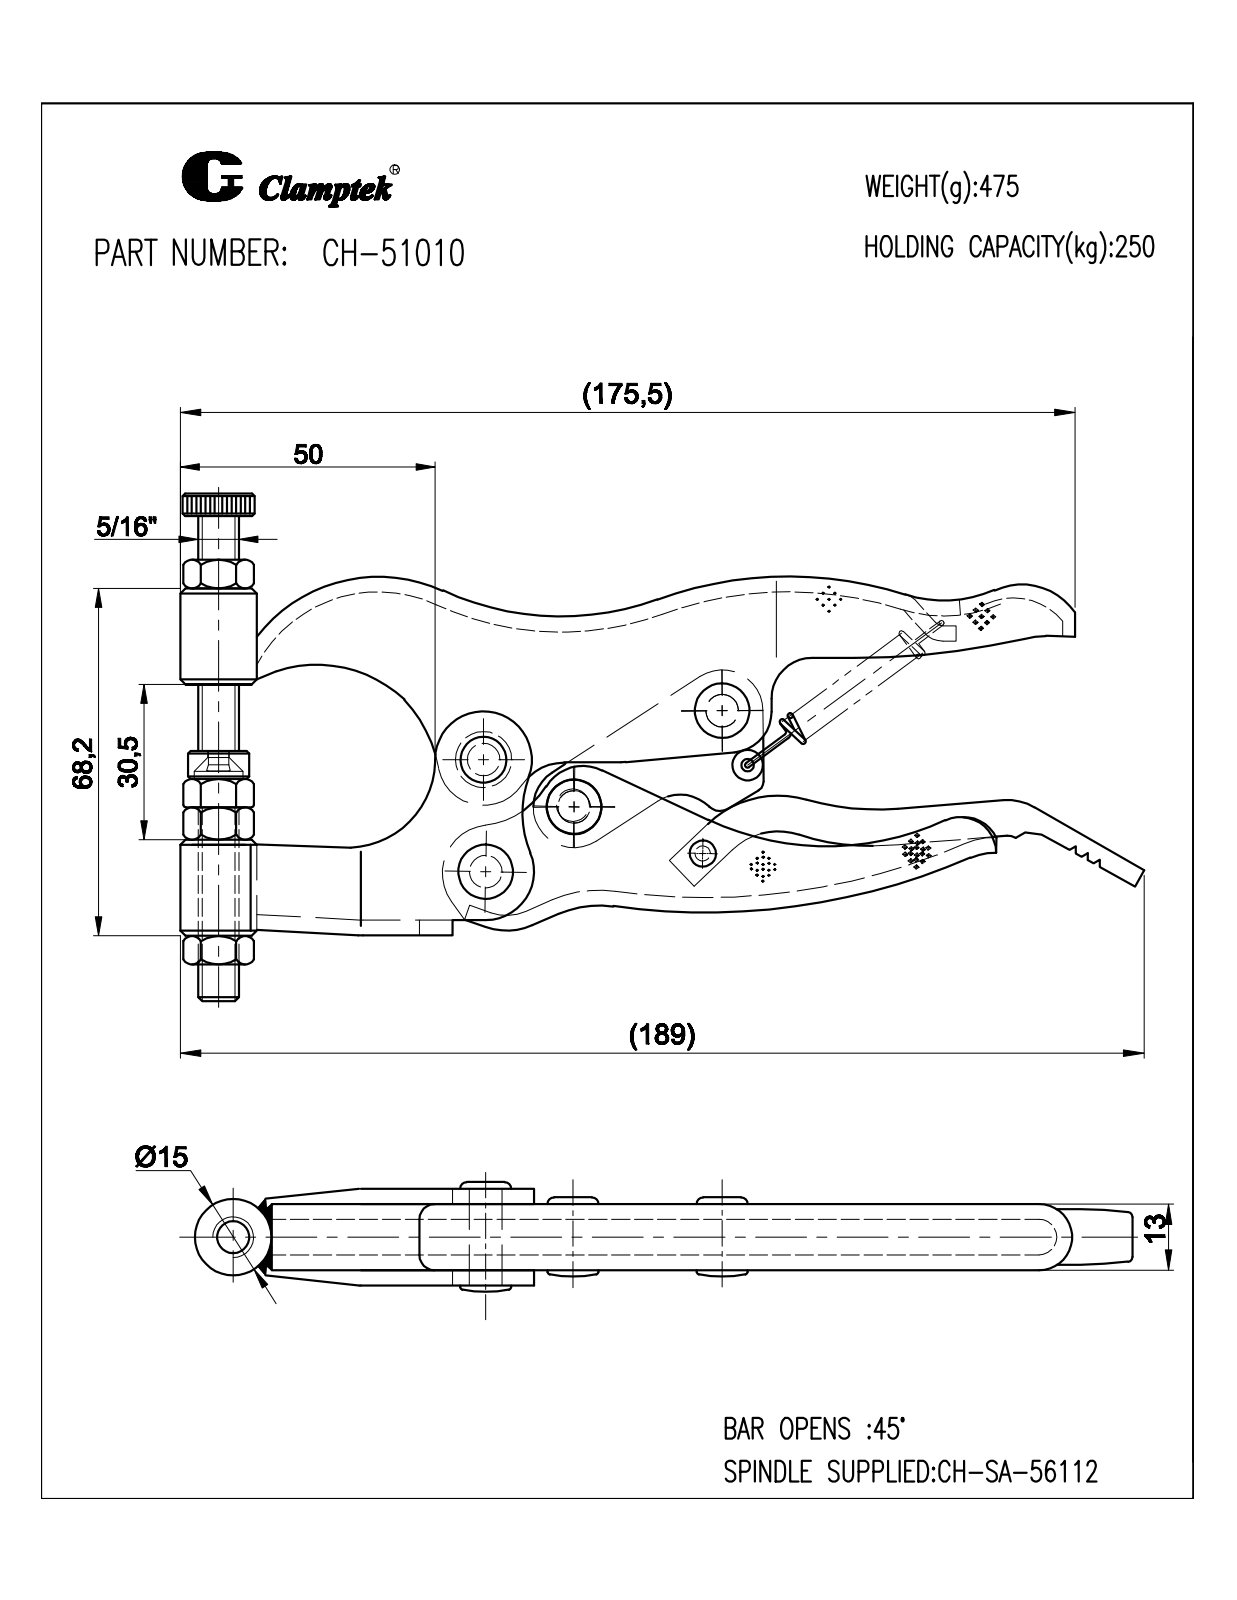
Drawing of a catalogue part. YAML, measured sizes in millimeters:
part_name: "CH-51010"
step_written_by: "SolidWorks 2008 (CONFIG_CONTROL_DESIGN)"
units: millimeters
bodies: {solids: 21, faces: 1258, planar: 436, cylindrical: 420, other: 402}
overall_size: [188.17, 100.47, 22]
volume: 39796
surface_area: 51355
round_holes:
  - {diameter: 6.4, count: 4}
  - {diameter: 5.56, count: 2}
  - {diameter: 5.61, count: 2}
  - {diameter: 6.5, count: 2}
  - {diameter: 15, count: 2}
  - {diameter: 1.46, count: 1}
  - {diameter: 2.33, count: 1}
  - {diameter: 2.5, count: 1}
  - {diameter: 3, count: 1}
  - {diameter: 4, count: 1}
  - {diameter: 9.6, count: 1}
round_bosses_or_shafts:
  - {diameter: 10, count: 4}
  - {diameter: 7, count: 2}
  - {diameter: 13.8, count: 1}
  - {diameter: 12, count: 1}
  - {diameter: 7.92, count: 1}
  - {diameter: 7.9, count: 1}
  - {diameter: 5, count: 1}
  - {diameter: 3, count: 1}
partial_cylinders:
  - {radius: 1, count: 7}
  - {radius: 3.5, count: 5}
  - {radius: 8, count: 5}
  - {radius: 6.5, count: 4}
  - {radius: 0.5, count: 3}
  - {radius: 1.5, count: 3}
  - {radius: 9.5, count: 3}
  - {radius: 2, count: 2}
face_to_face_distances: [3, 10, 13, 7, 6, 16, 19, 4, 9, 1]
hole_center_spacings: [11.79, 12.32, 16.56, 18.45, 19.51, 21.52, 22, 22.22]
